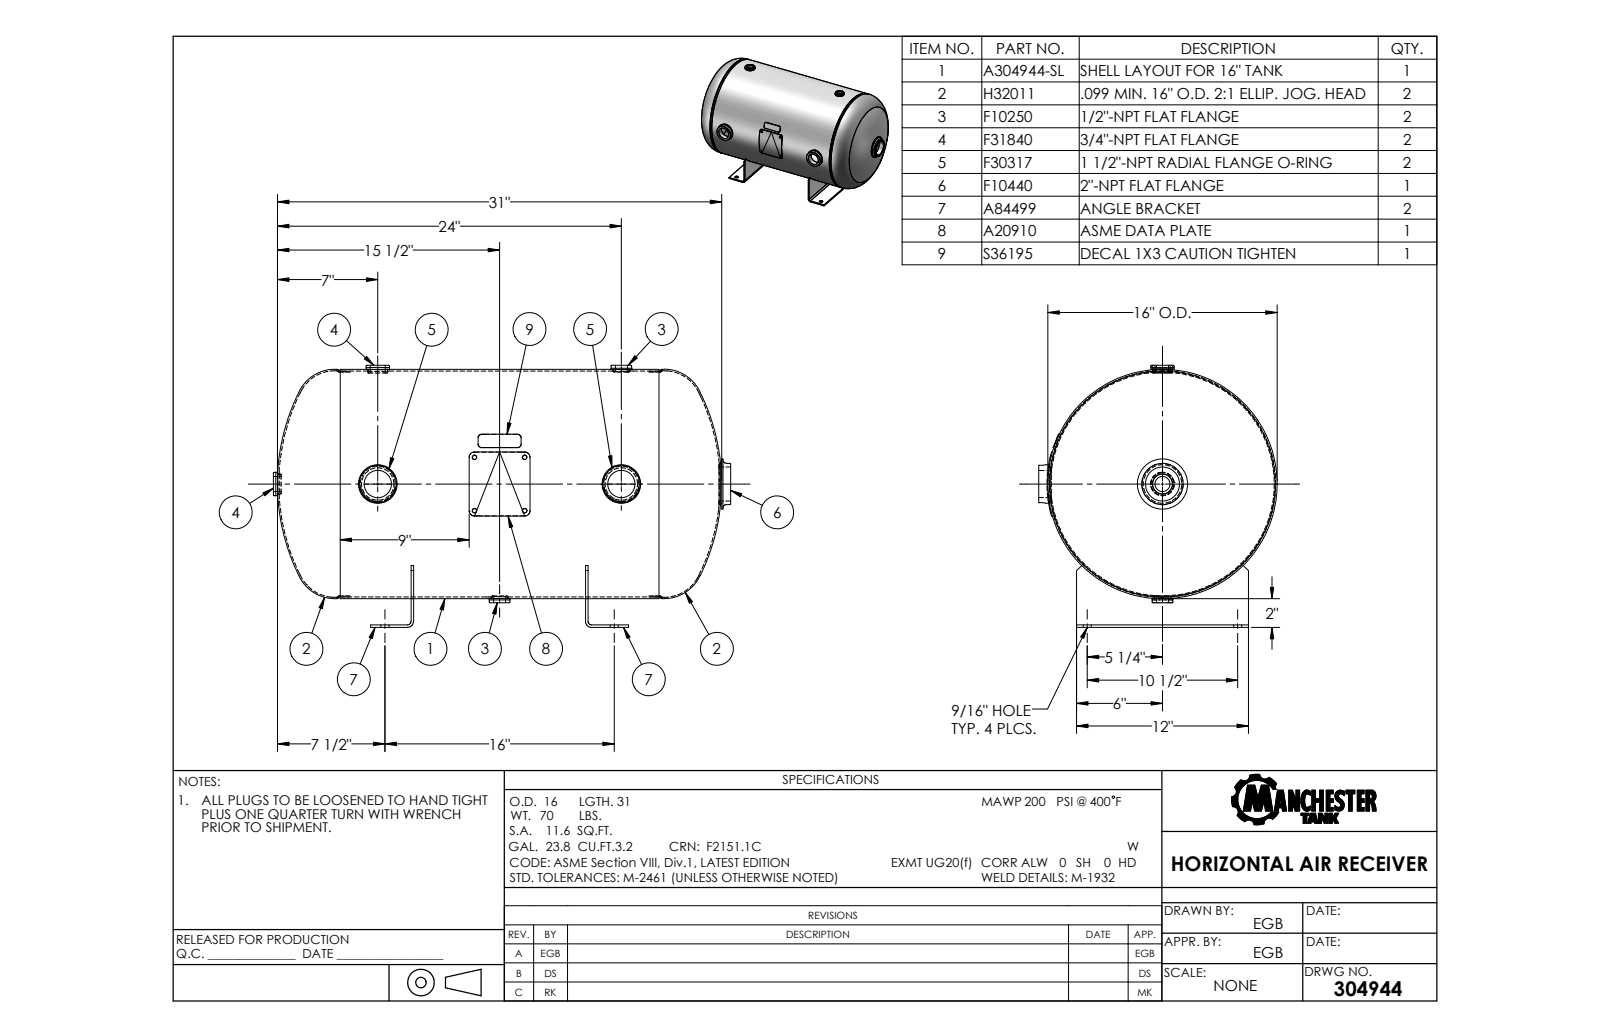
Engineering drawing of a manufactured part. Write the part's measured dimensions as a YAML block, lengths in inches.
part_name: "304944"
step_written_by: "SolidWorks 2012 (CONFIG_CONTROL_DESIGN)"
units: inches
bodies: {solids: 0, faces: 244, planar: 103, cylindrical: 63, other: 78}
overall_size: [31.781, 18.844, 17.385]
round_holes:
  - {diameter: 0.563, count: 4}
round_bosses_or_shafts:
  - {diameter: 2.688, count: 2}
  - {diameter: 1.9, count: 2}
  - {diameter: 1.63, count: 2}
  - {diameter: 1.45, count: 2}
  - {diameter: 1.438, count: 2}
  - {diameter: 1.05, count: 2}
  - {diameter: 0.84, count: 2}
  - {diameter: 16, count: 1}
partial_cylinders:
  - {radius: 0.25, count: 4}
  - {radius: 0.429, count: 2}
  - {radius: 8.06, count: 1}
face_to_face_distances: [0.179, 12.179, 12, 12.358, 4.196, 4.375, 16.375, 16.554, 20.75, 0.125]
hole_center_spacings: [10.5, 16, 19.138]
